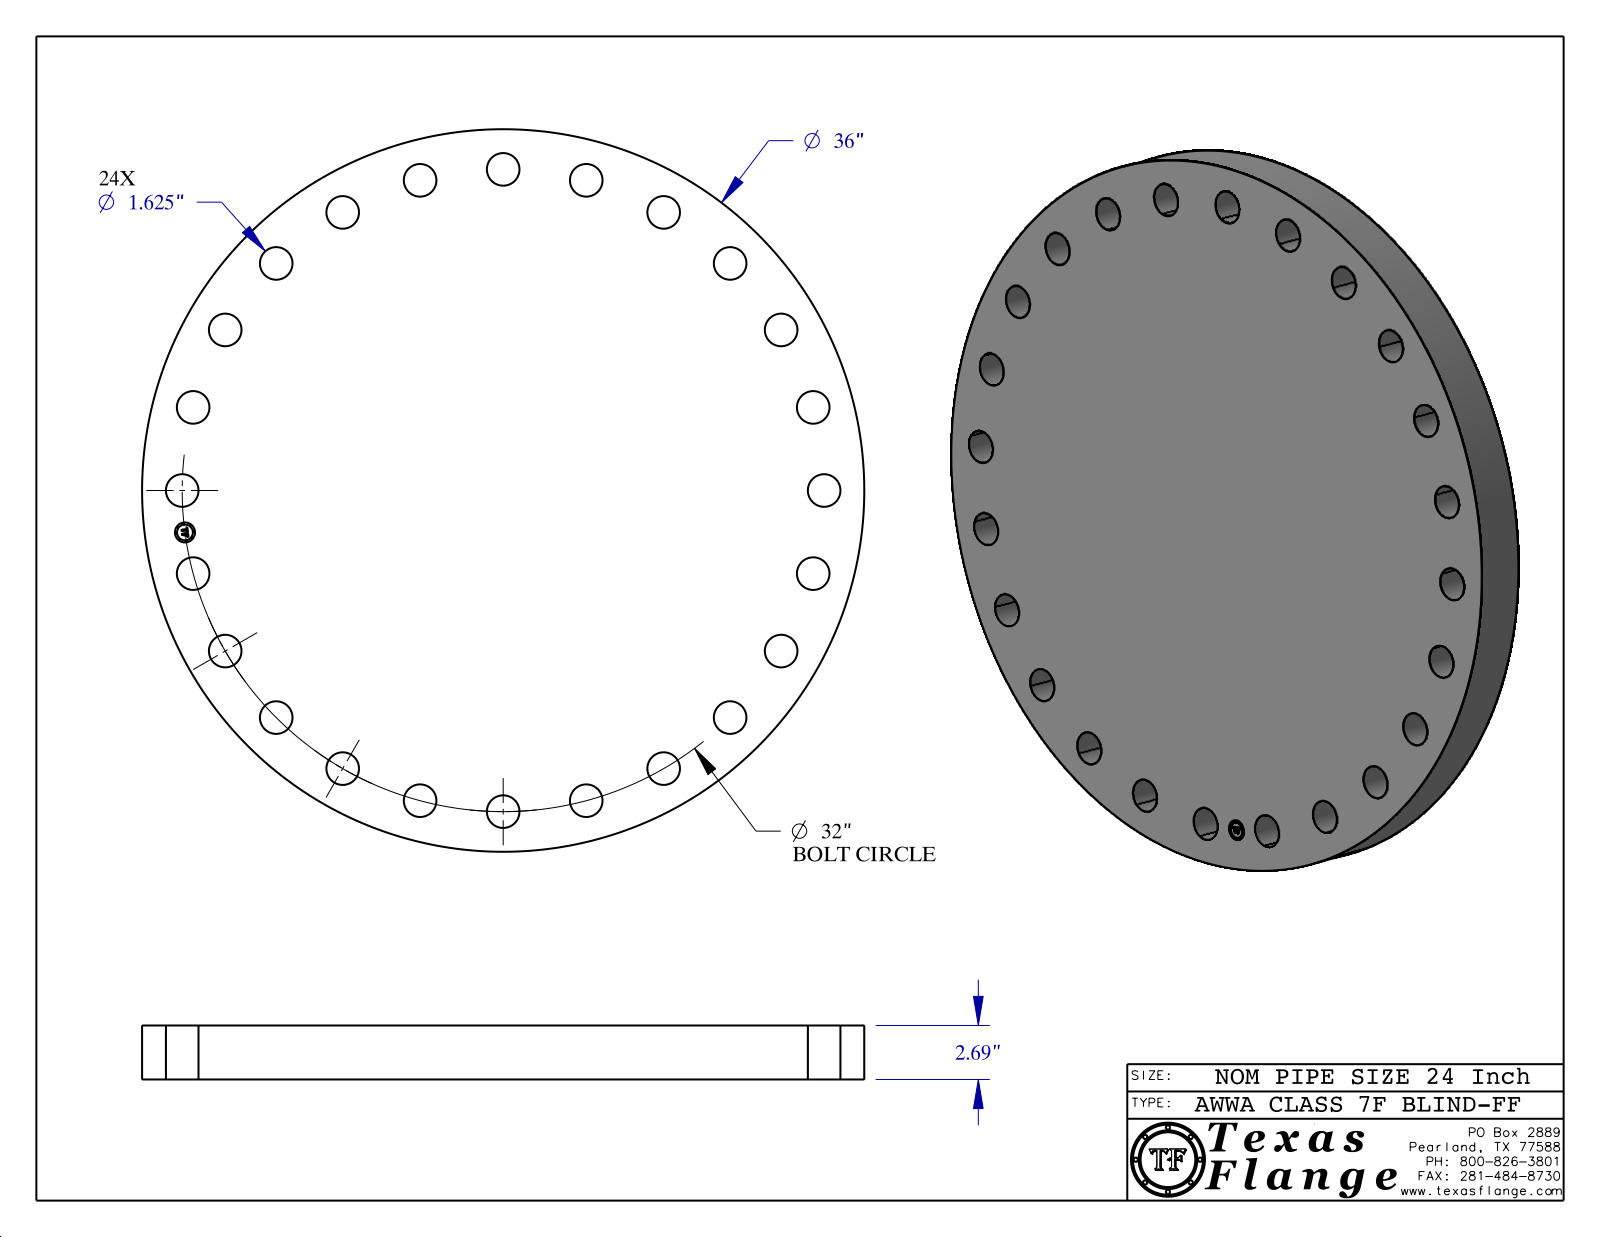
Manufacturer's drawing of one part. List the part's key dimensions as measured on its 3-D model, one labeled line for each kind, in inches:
Part name (STEP PRODUCT): AWWA Class 7F-BLIND-FF
STEP written by: CATIA V5 STEP AP214 (AUTOMOTIVE_DESIGN)
Units: inches
Bodies: 1 solid, 437 faces (367 planar, 70 cylindrical, 0 other)
Overall size (bounding box): 36 × 36 × 2.69
Volume: 2 604 in³ · Surface area: 2 570 in²
Round holes (diameter × count): ⌀1.625 ×24, ⌀1 ×1
Round bosses / shafts (diameter × count): ⌀0.061 ×8, ⌀36 ×1, ⌀0.788 ×1
Main face-to-face distances: 2.69, 0.015, 2.675, 0.298, 0.292, 0.054, 0.193, 0.248, 0.044, 0.15
Hole centre spacings: 16, 30.909, 4.177, 8.282, 12.246, 19.48, 22.627, 25.387
